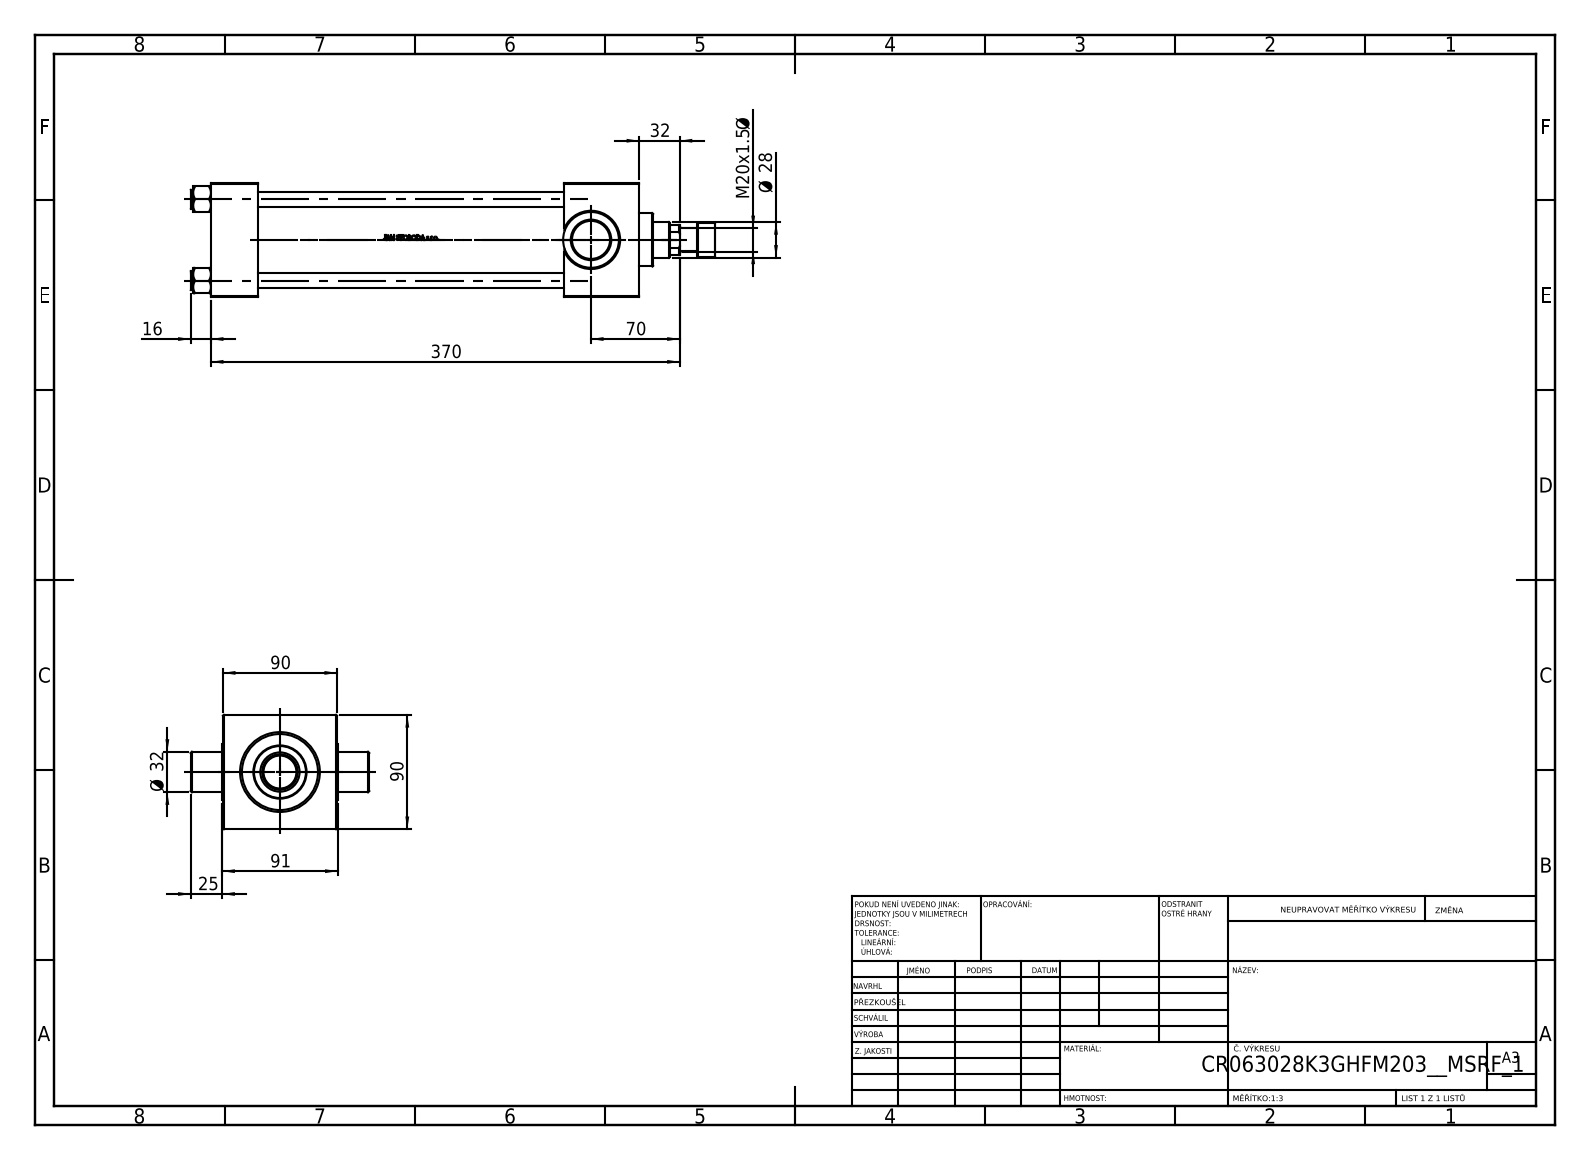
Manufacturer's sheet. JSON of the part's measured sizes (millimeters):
{"part_name": "V215_VC_A; V215CR_ROD_END_F; V215CR_VCP_K; V215CR_K_TYCINKA (+2 more)", "step_written_by": "SolidWorks 2019 (CONFIG_CONTROL_DESIGN)", "units": "millimeters", "bodies": {"solids": 12, "faces": 1079, "planar": 433, "cylindrical": 116, "other": 530}, "overall_size": [414, 141, 90], "volume_mm3": 1325000, "surface_area_mm2": 299648, "round_holes": [[12, 4], [7, 1], [18.5, 1], [28, 1], [31, 1], [50, 1], [60, 1], [63, 1]], "round_bosses_or_shafts": [[15, 4], [69, 1], [42, 1], [32, 1], [27, 1], [18, 1]], "partial_cylinders_radius": [[22, 1]], "face_to_face_distances": [90, 37, 0.5, 89.5, 338, 301, 242, 279, 59, 89], "hole_center_spacings": [45.47, 64.3, 90.93]}
